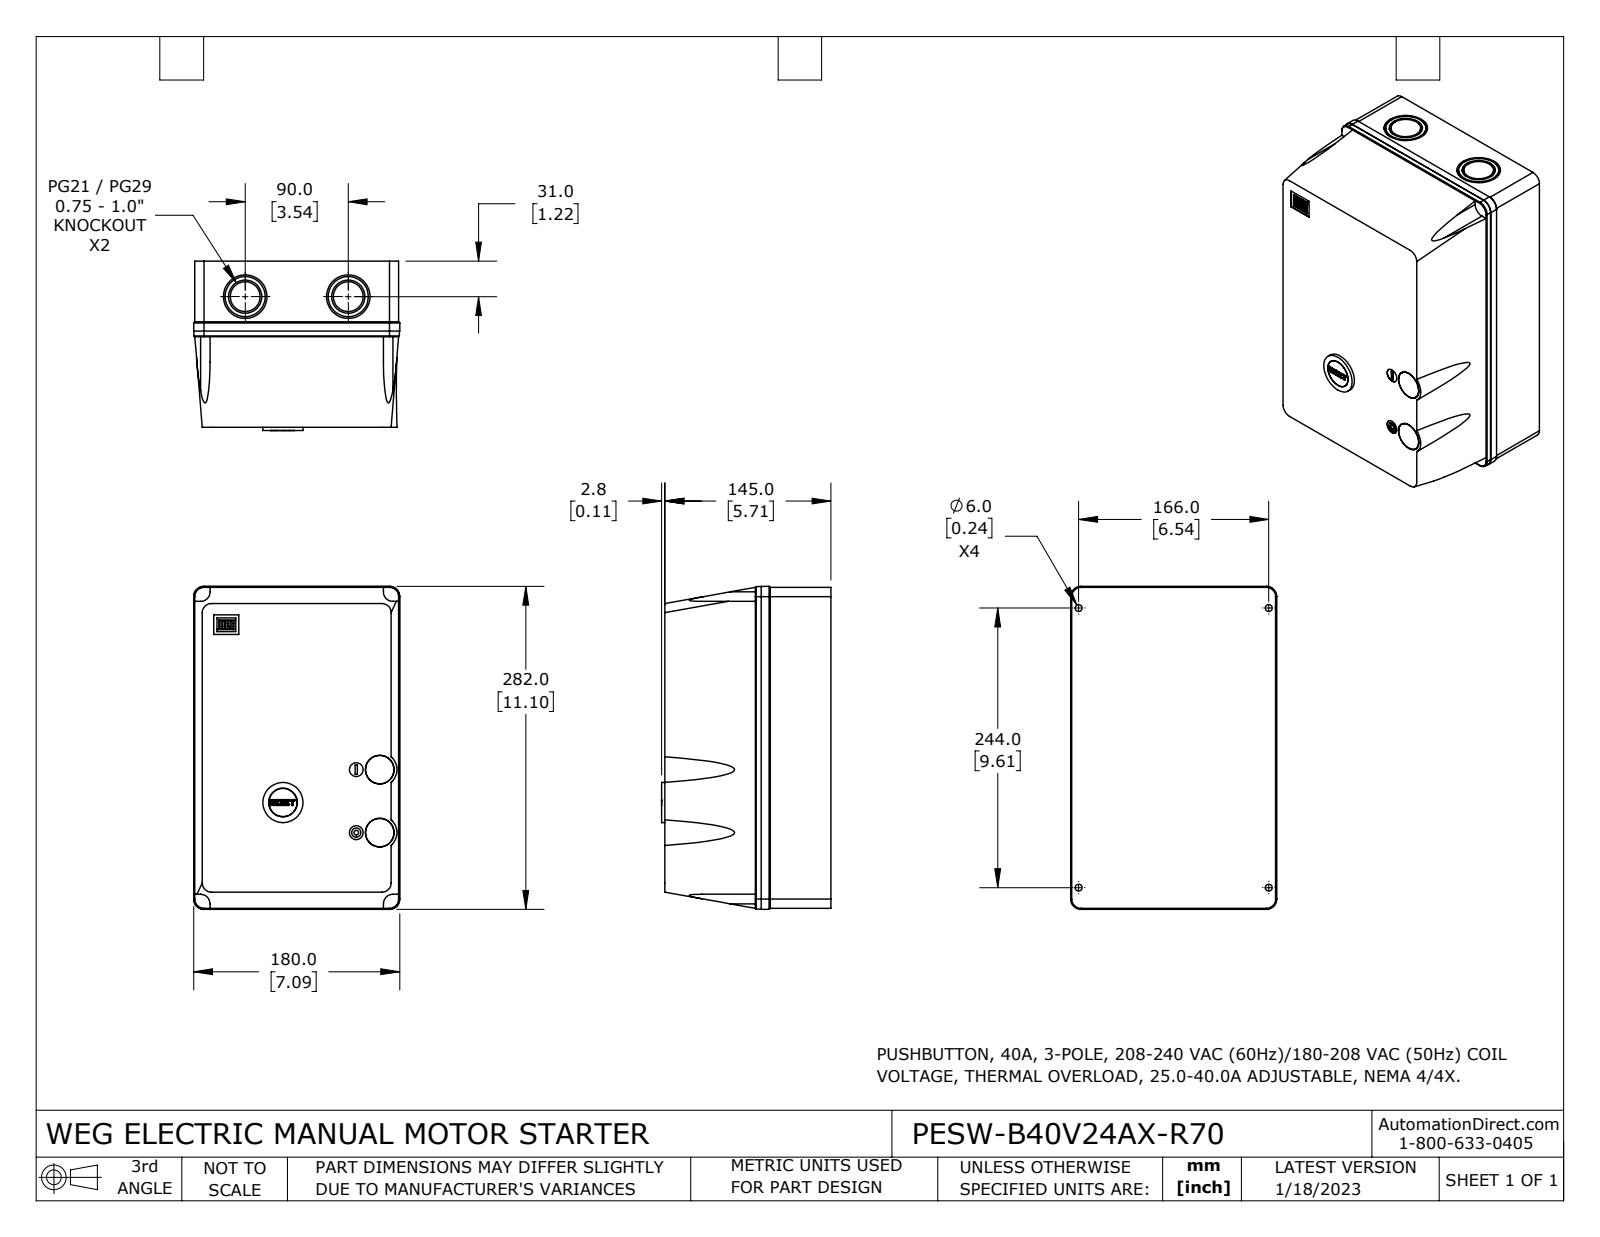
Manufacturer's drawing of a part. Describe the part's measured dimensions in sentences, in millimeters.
The part is named "PESW-B40V24AX-R70". Its 3-D file was written by "SolidWorks 2021 (CONFIG_CONTROL_DESIGN)". It is 3 solids with 286 faces: 130 planar, 144 cylindrical and 12 other. Overall it measures 282 by 180 by 147.9 millimeters. Its volume is 7 014 000 cubic millimeters and its surface area 232 257 square millimeters. Round holes: 4 of diameter 6, 3 of diameter 25, 2 of diameter 12, 2 of diameter 29, 2 of diameter 38, 1 of diameter 4, 1 of diameter 30.5. Round bosses or shafts: 3 of diameter 35, 2 of diameter 26, 2 of diameter 24.8, 1 of diameter 30.3, 1 of diameter 24.6, 1 of diameter 14, 1 of diameter 8. Partial cylindrical surfaces (rounded edges, fillets, slot ends): 34 of radius 0.1, 4 of radius 8, 4 of radius 8.3, 4 of radius 8.7, 4 of radius 9, 1 of radius 1.6. The main face-to-face distances are 145, 178, 280, 1, 0.7, 179, 179.7, 178.7, 281, 180. The hole center spacings are 20.5, 55, 58.7, 166, 244, 295.11, 49.14, 57.14.
